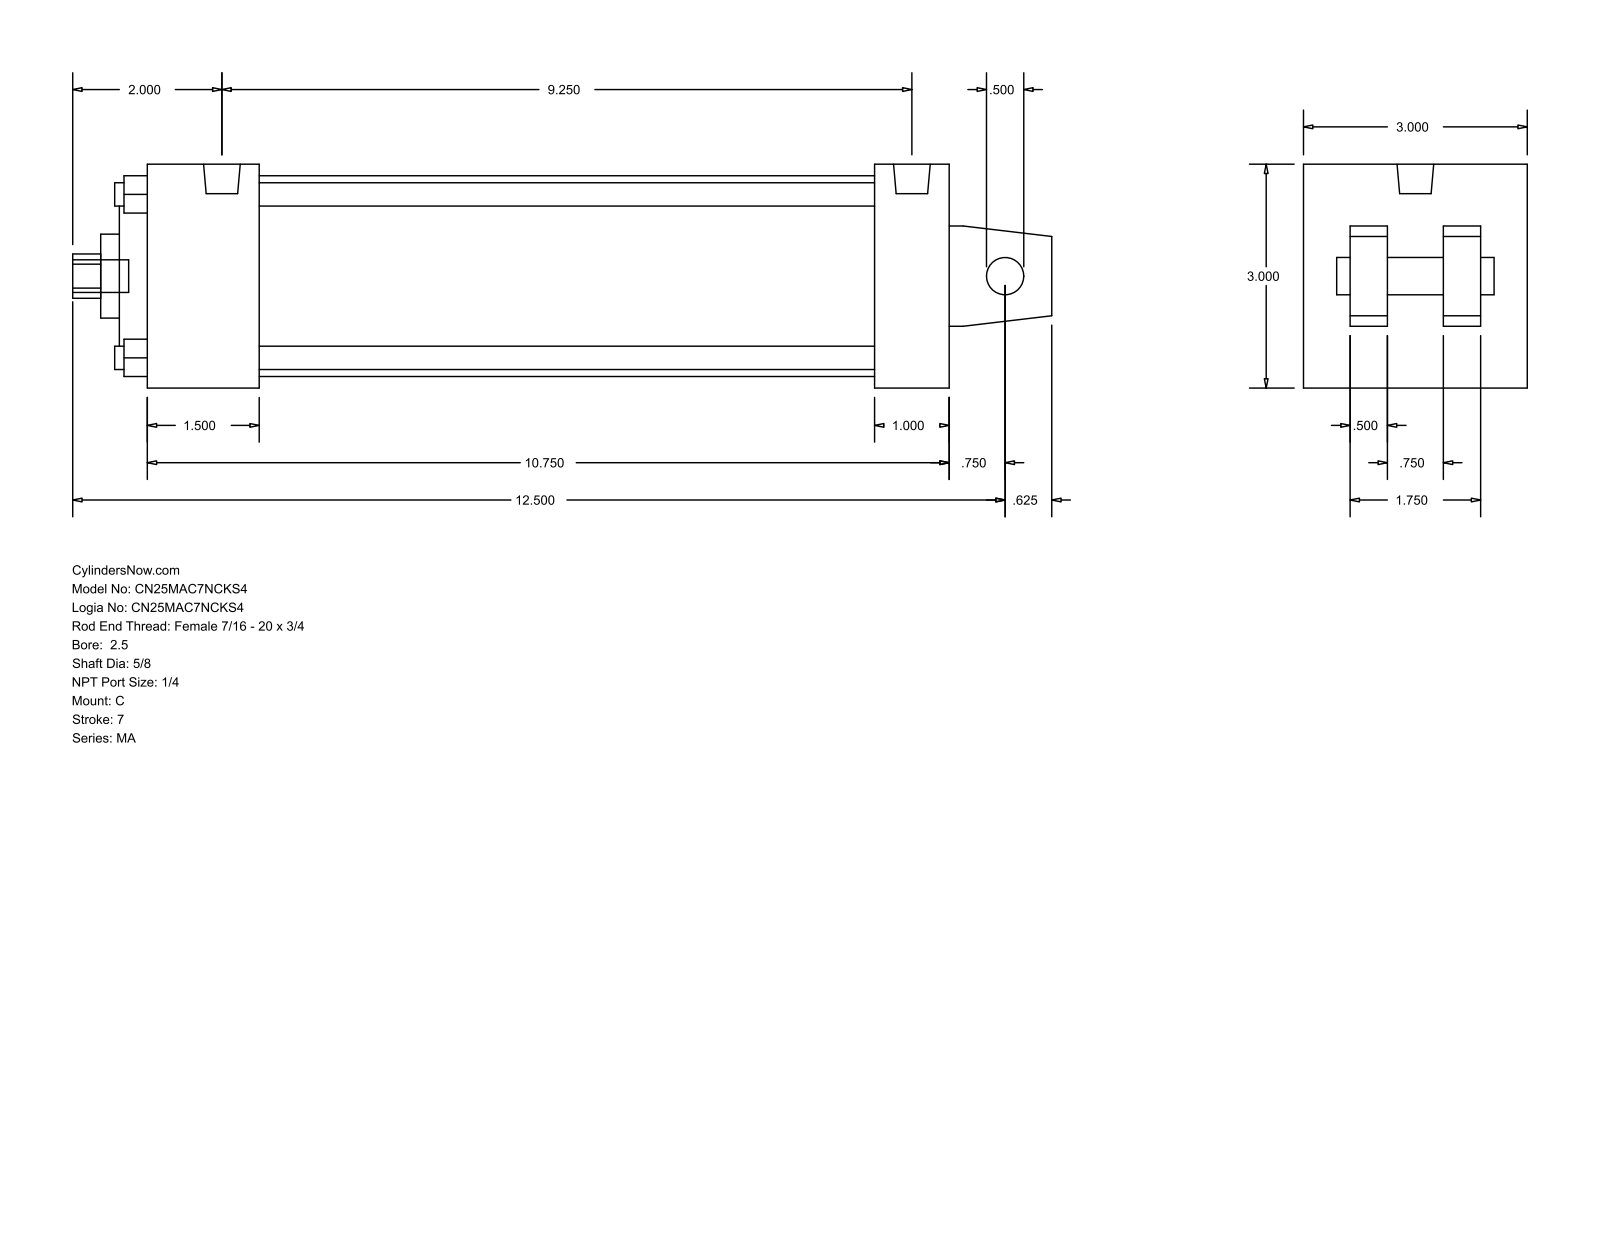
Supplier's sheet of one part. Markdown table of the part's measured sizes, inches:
| quantity | value |
| --- | --- |
| part name | MA_C__0250_0.625 |
| STEP written by | GSSL Pune (CONFIG_CONTROL_DESIGN) |
| units | inches |
| bodies | 0 solids, 105 faces (77 planar, 28 cylindrical, 0 other) |
| overall size | 13.125 × 3 × 3 |
| round holes (diameter × count) | 0.313 × 4, 0.5 × 1, 0.625 × 1, 1.125 × 1, 2 × 1, 2.69 × 1 |
| round bosses / shafts (diameter × count) | 0.313 × 4, 0.492 × 2, 0.437 × 1 |
| partial cylindrical surfaces (radius × count) | 0.297 × 1 |
| main face-to-face distances | 3, 10.75, 0.5, 0.625, 2.375, 1.875, 1, 1.5, 9.75, 8.25 |
| hole center spacings | 1.548, 2.19, 3.097 |
